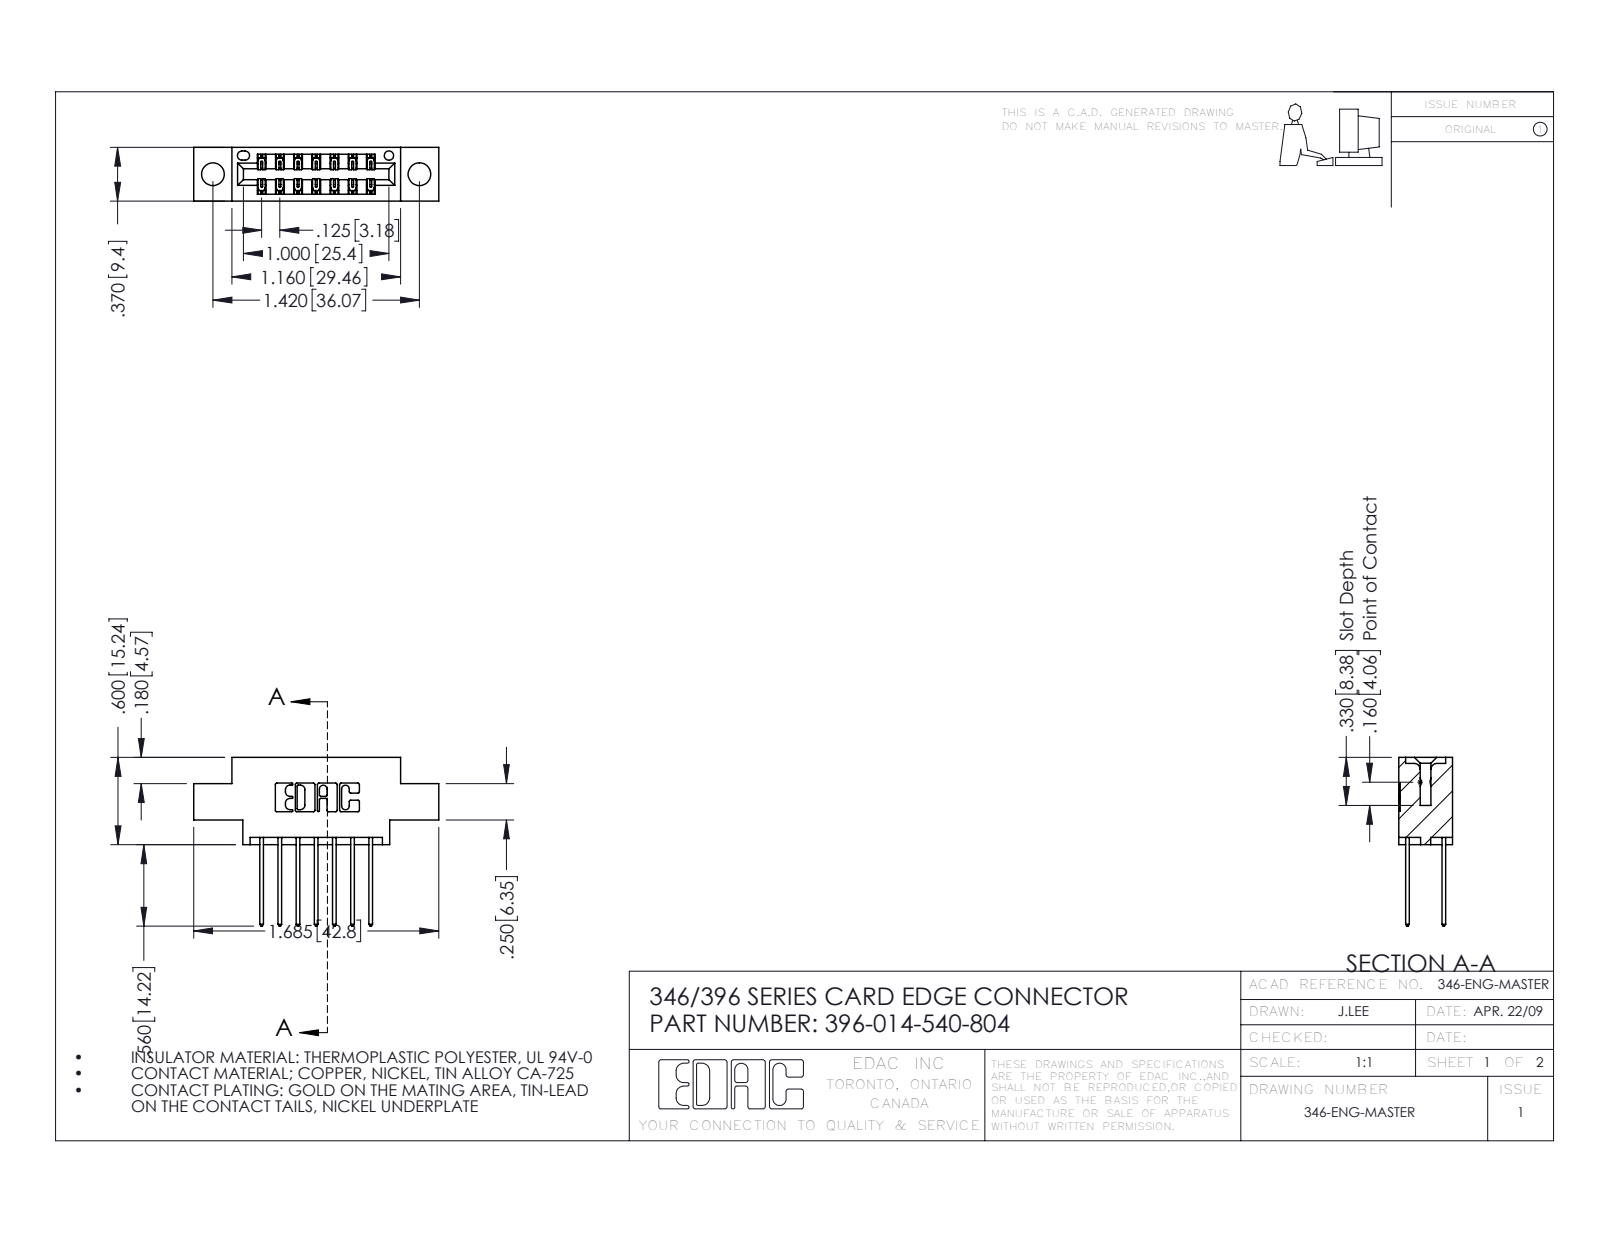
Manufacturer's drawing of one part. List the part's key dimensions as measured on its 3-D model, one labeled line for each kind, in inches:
Part name (STEP PRODUCT): 345-292-001_345-293-140; 396-014-540-804; 346 Part_0.170 Offset - 0.156 Dia-TH
STEP written by: SolidWorks 2016 (CONFIG_CONTROL_DESIGN)
Units: inches
Bodies: 15 solids, 854 faces (570 planar, 284 cylindrical, 0 other)
Overall size (bounding box): 1.685 × 1.16 × 0.37
Volume: 0.227 in³ · Surface area: 7.435 in²
Round holes (diameter × count): ⌀0.156 ×2, ⌀0.064 ×1
Partial cylindrical surfaces — rounded edges, fillets, slot ends (radius × count): R0.01 ×22, R0.006 ×21, R0.01 ×14, R0.007 ×6, R0.031 ×6, R0.026 ×3, R0.014 ×2, R0.022 ×2
Main face-to-face distances: 0.25, 0.048, 0.322, 0.37, 0.072, 0.298, 0.025, 0.275, 0.225, 0.148
Hole centre spacings: 0.246, 1.217, 1.42
